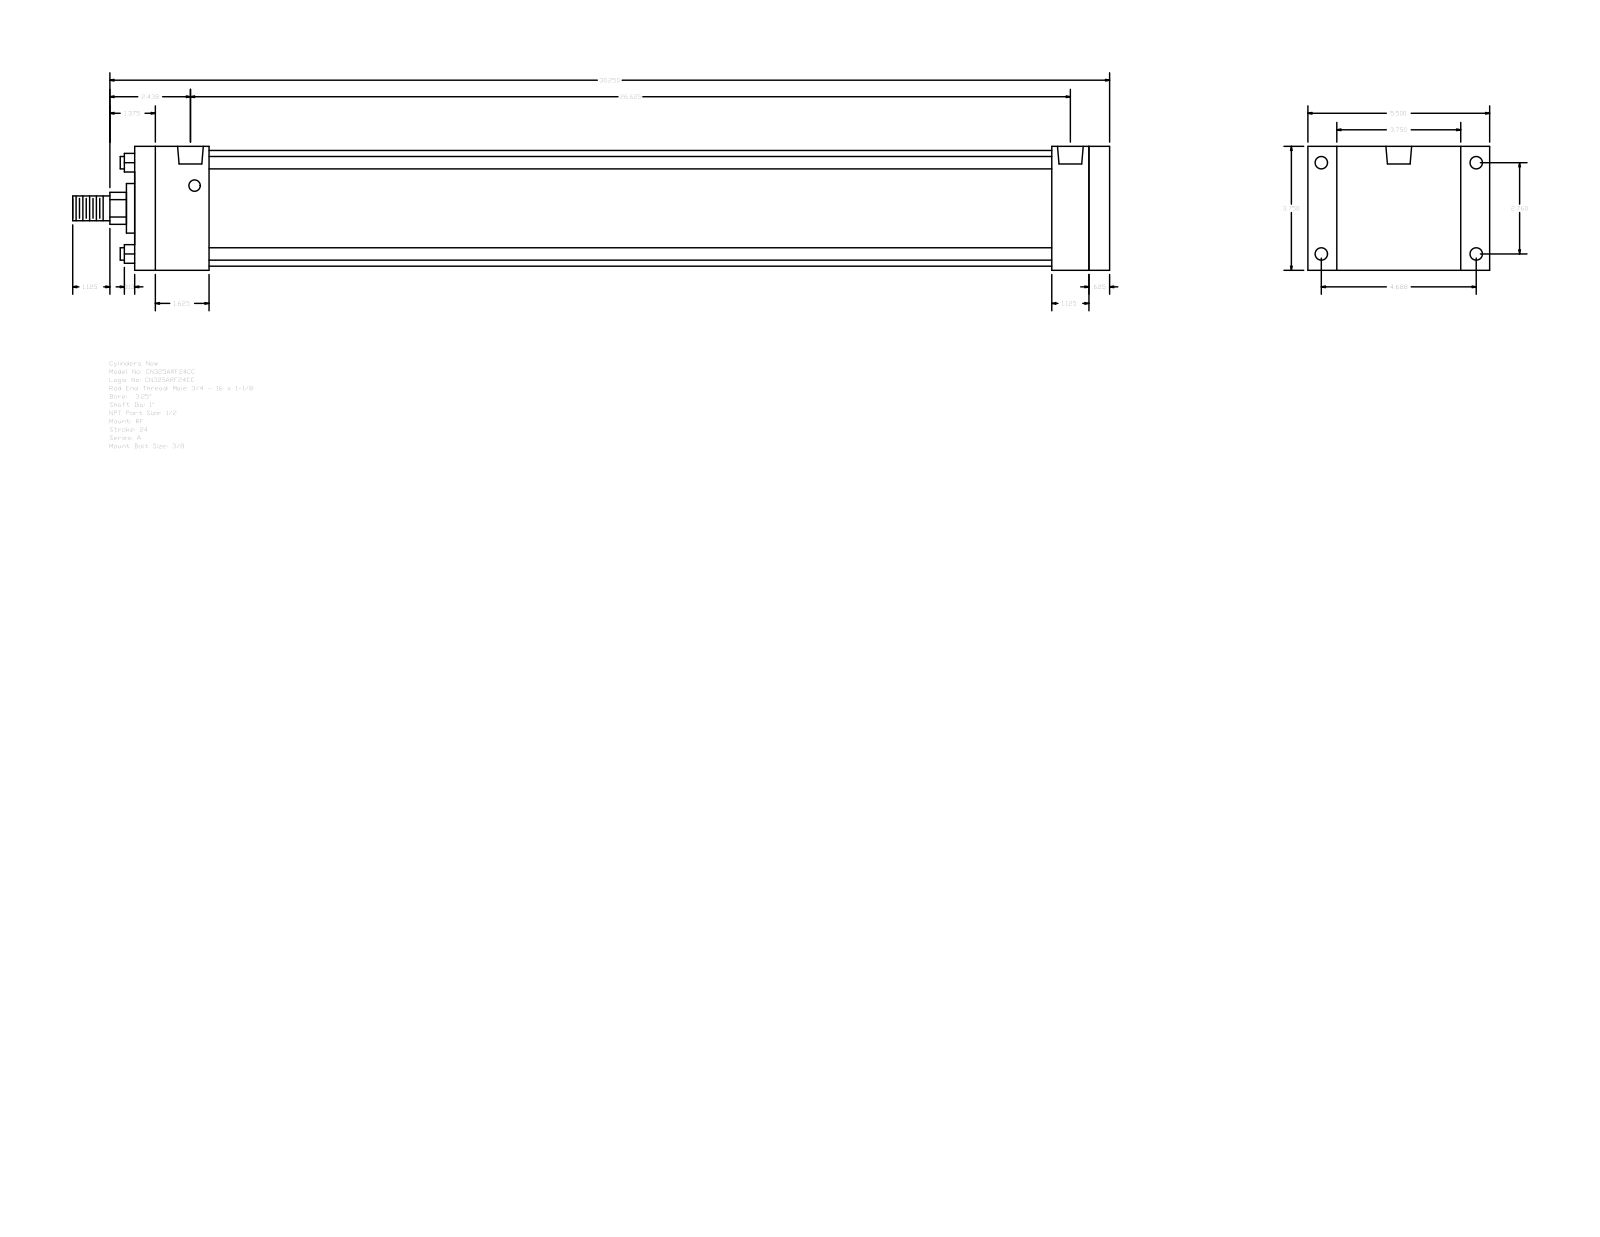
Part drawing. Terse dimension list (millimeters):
name: A_RF__0325_1
written by: GSSL Pune (CONFIG_CONTROL_DESIGN)
unit: mm
bodies: 0 solids, 92 faces (64 planar, 28 cylindrical, 0 other)
size: 796.92 × 139.7 × 95.25
holes: 4× ⌀8.73, 4× ⌀9.53, 2× ⌀19.77
bosses: 4× ⌀9.53, 1× ⌀88.9, 1× ⌀38.1, 1× ⌀25.4, 1× ⌀19.05
rounds: 1× R12.29
face distances: 95.24, 749.3, 733.43, 15.87, 22.23, 117.47, 704.85, 28.58, 44.45, 57.15
hole spacings: 3.18, 70.1, 119.06, 138.16, 669.92, 673.1, 676.28
